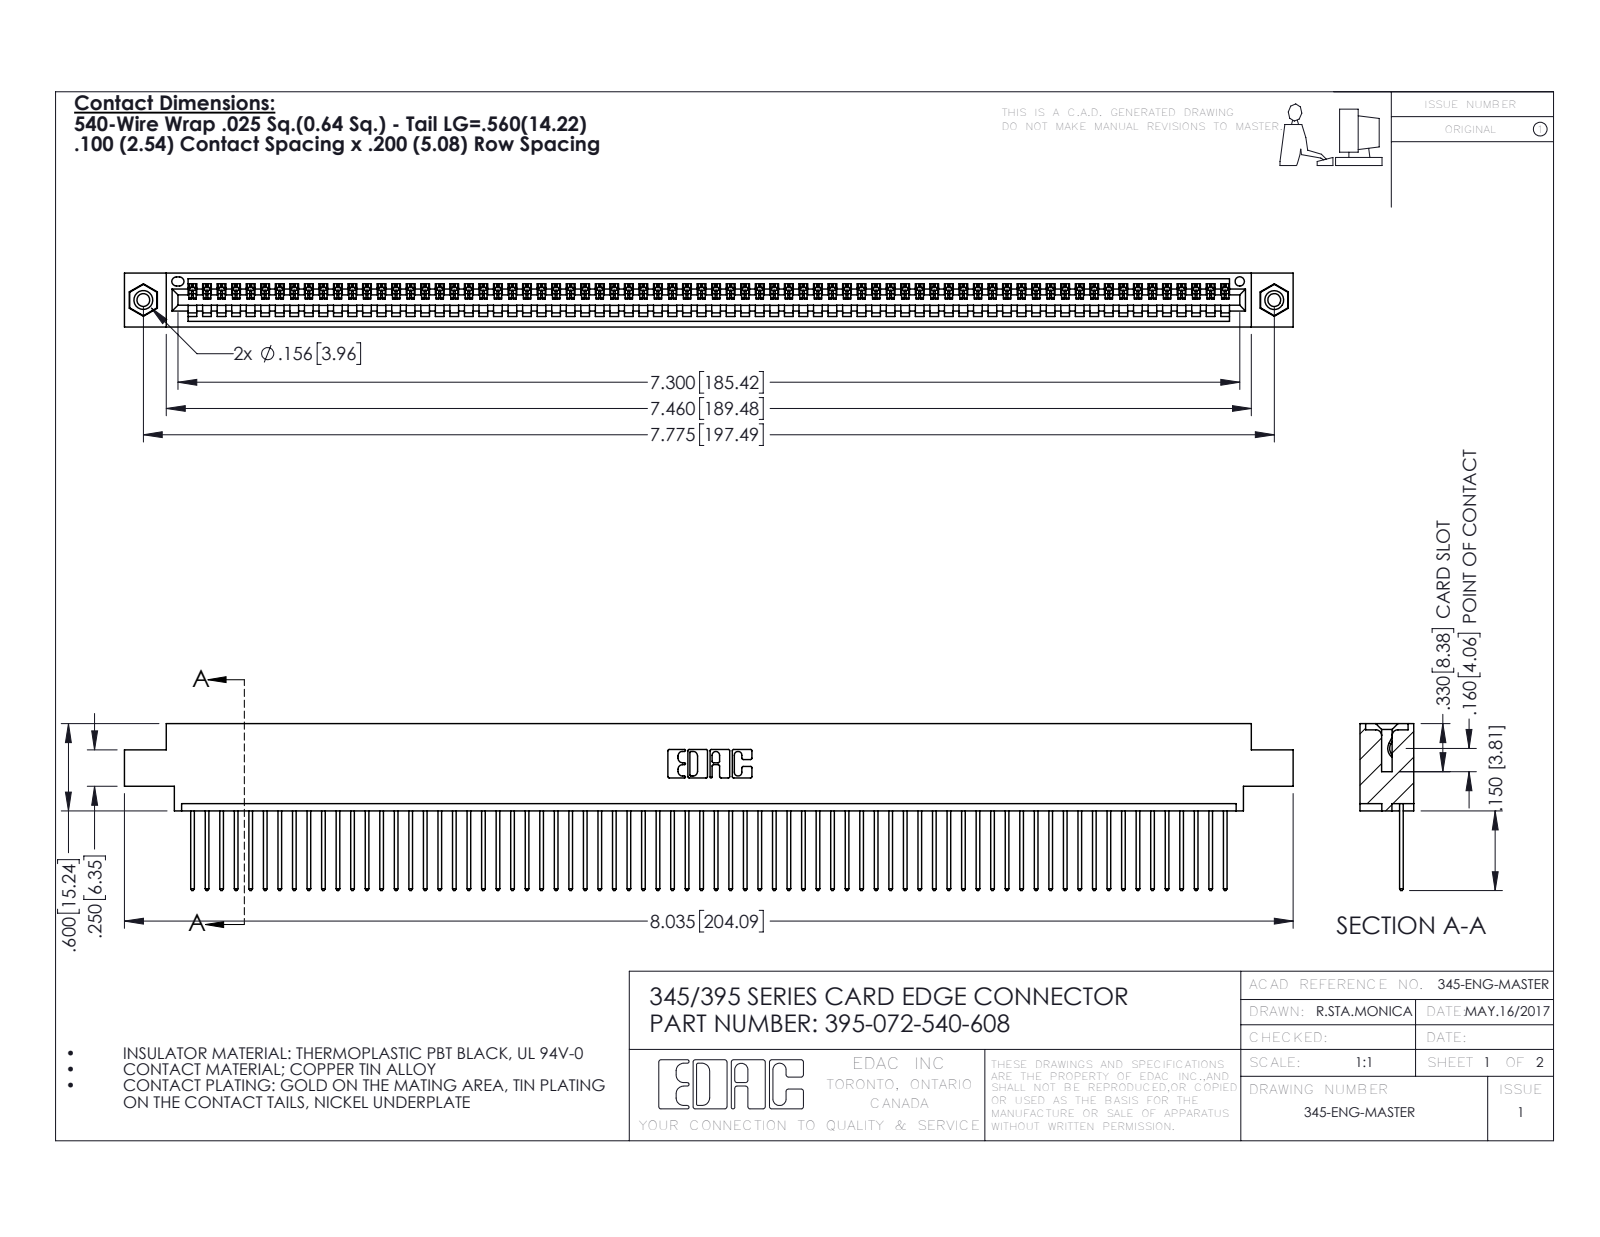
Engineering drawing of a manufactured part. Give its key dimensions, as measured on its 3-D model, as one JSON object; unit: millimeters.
{"part_name": "345 Part_0.170 Offset - 0.156 Dia-TI; 345-292-001_345-293-140; 345-250-001_345-250-003-102; 395-072-540-608", "step_written_by": "SolidWorks 2016 (CONFIG_CONTROL_DESIGN)", "units": "millimeters", "bodies": {"solids": 75, "faces": 4366, "planar": 2996, "cylindrical": 1354, "other": 16}, "overall_size": [204.1, 29.1, 9.4], "volume_mm3": 19620, "surface_area_mm2": 27310, "round_holes": [[2.3, 2], [3.2, 2], [4, 2], [1.6, 1]], "round_bosses_or_shafts": [[3.9, 2]], "partial_cylinders_radius": [[0.2, 144], [0.3, 144], [0.3, 22], [0.2, 6], [0.8, 6], [0.7, 3], [0.8, 2], [1, 2]], "face_to_face_distances": [1.8, 7.6, 9.4, 2.5, 6.9, 0.6, 5.1, 5.7, 3.8, 4.4], "hole_center_spacings": [6.9, 191.5, 197.5]}
